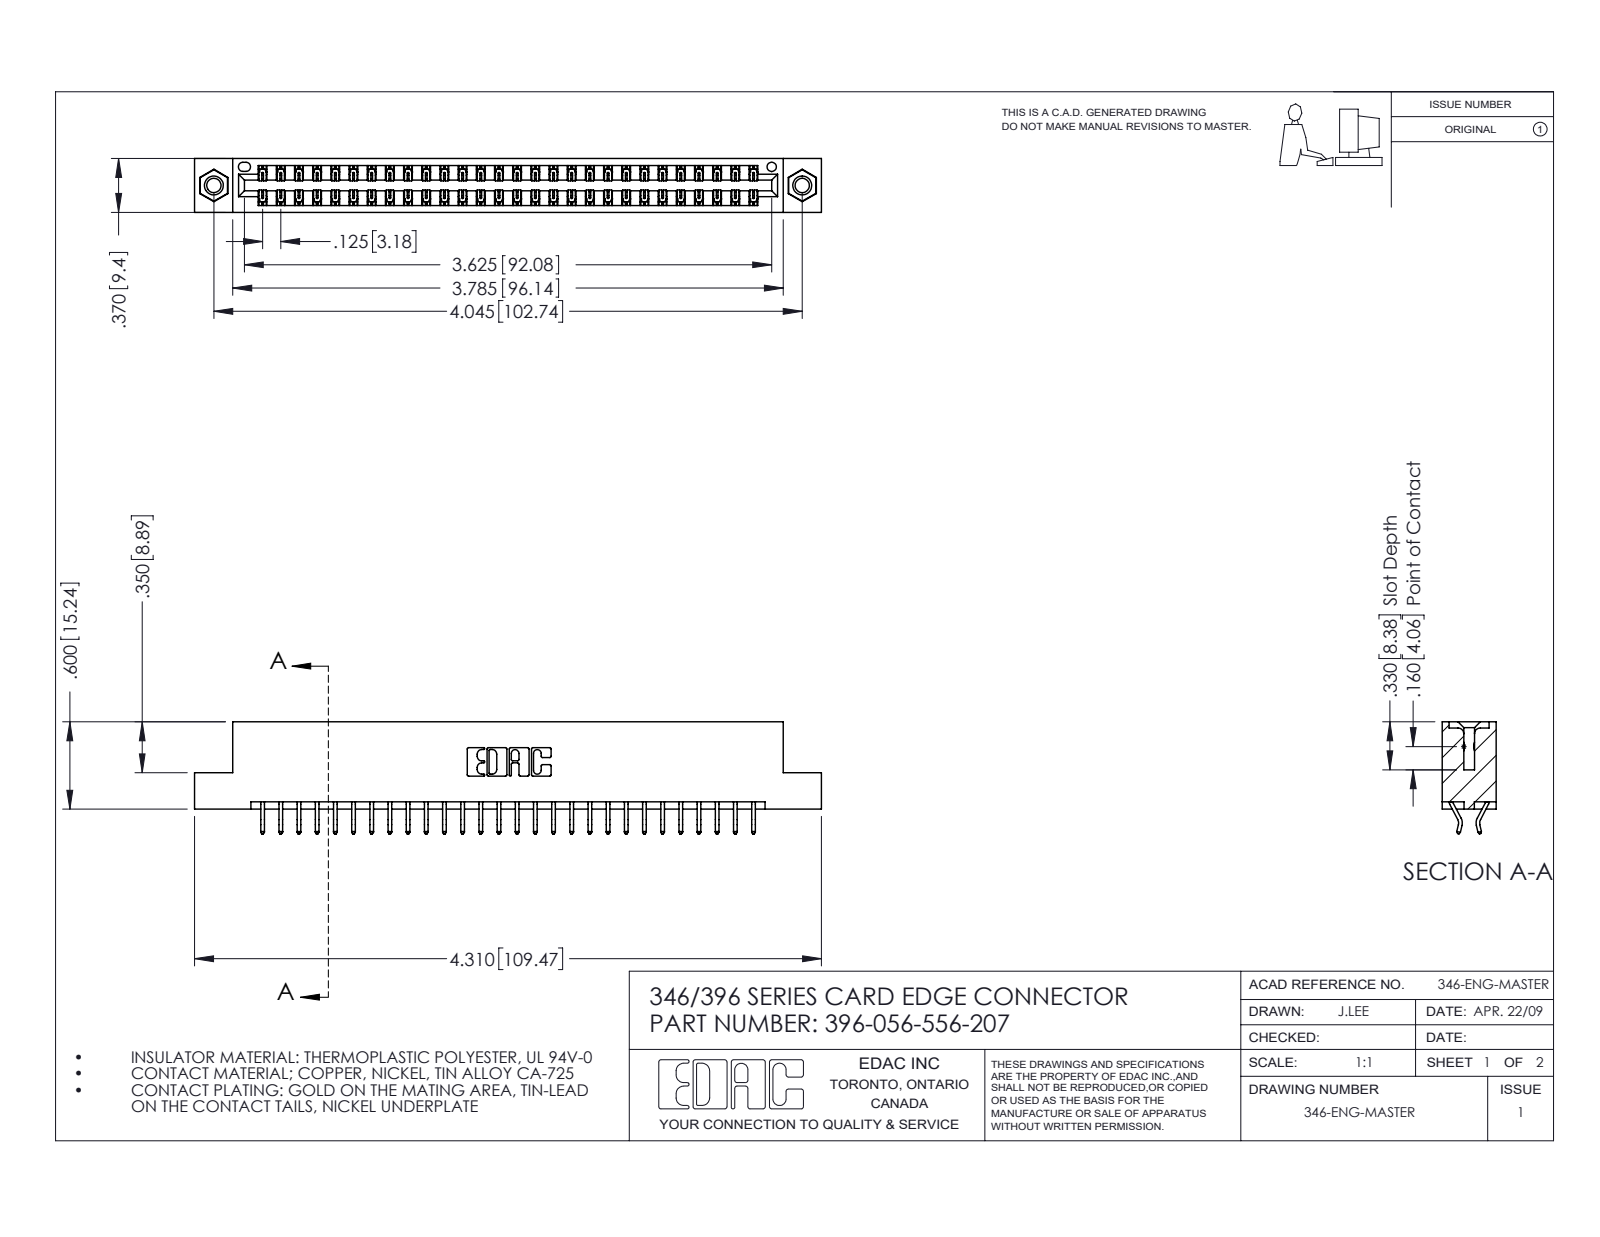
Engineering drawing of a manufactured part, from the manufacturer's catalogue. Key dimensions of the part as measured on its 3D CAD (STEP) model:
Part name (STEP PRODUCT): 345-250-001_345-250-005-103; 346 Part_Flush Mounting Lugs - 0.156 Dia-TI; 345-292-001_556 Tail; 396-056-556-207
STEP written by: SolidWorks 2016 (CONFIG_CONTROL_DESIGN)
Units: inches
Bodies: 59 solids, 3430 faces (2292 planar, 1122 cylindrical, 16 other)
Overall size (bounding box): 4.31 × 0.77 × 0.37
Volume: 0.644 in³ · Surface area: 22.11 in²
Round holes (diameter × count): ⌀0.098 ×2, ⌀0.125 ×2, ⌀0.156 ×2, ⌀0.064 ×1
Round bosses / shafts (diameter × count): ⌀0.155 ×2
Partial cylindrical surfaces — rounded edges, fillets, slot ends (radius × count): R0.006 ×84, R0.01 ×22, R0.007 ×6, R0.031 ×6, R0.026 ×3, R0.01 ×2, R0.014 ×2, R0.022 ×2
Main face-to-face distances: 0.048, 0.322, 0.37, 0.25, 0.025, 0.072, 0.298, 0.275, 0.148, 0.222
Hole centre spacings: 0.246, 3.837, 4.045
